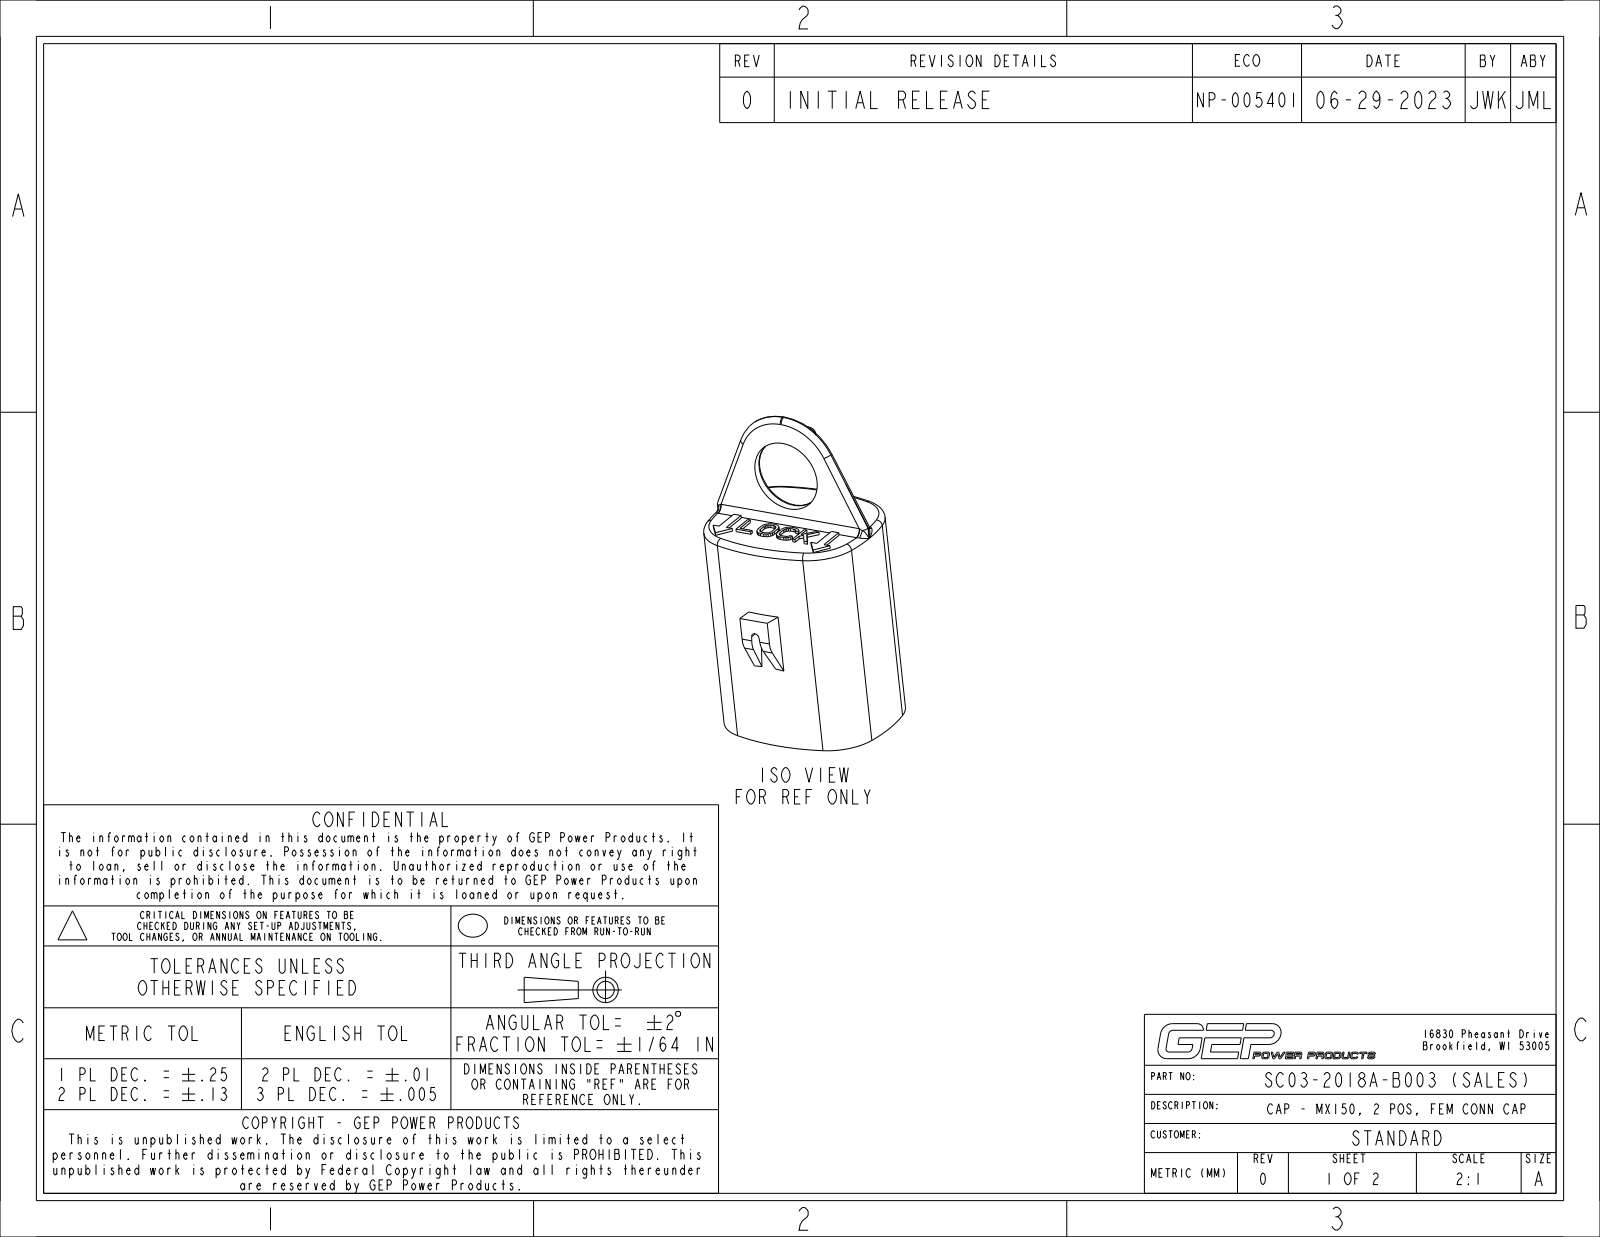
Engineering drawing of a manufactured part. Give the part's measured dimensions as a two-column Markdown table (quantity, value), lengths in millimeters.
| quantity | value |
| --- | --- |
| part name | PC03-2018A-B003_NCF; SC03-2018A-B003_NCF_ASM |
| STEP written by | CREO PARAMETRIC BY PTC INC, 2017110 (CONFIG_CONTROL_DESIGN) |
| units | millimeters |
| bodies | 1 solid, 440 faces (273 planar, 27 cylindrical, 140 other) |
| overall size | 29 × 15.33 × 14.42 |
| volume | 1 230 mm³ |
| surface area | 2 129 mm² |
| round holes (diameter × count) | 3 × 1, 6.35 × 1 |
| partial cylindrical surfaces (radius × count) | 4.17 × 4, 0.5 × 3, 0.3 × 2, 0.6 × 2, 13.84 × 2, 17.43 × 2, 0.38 × 1, 2 × 1 |
| main face-to-face distances | 1, 18, 19, 1.25, 19.25, 1.1, 18.15, 0.85, 18.25, 0.75 |
